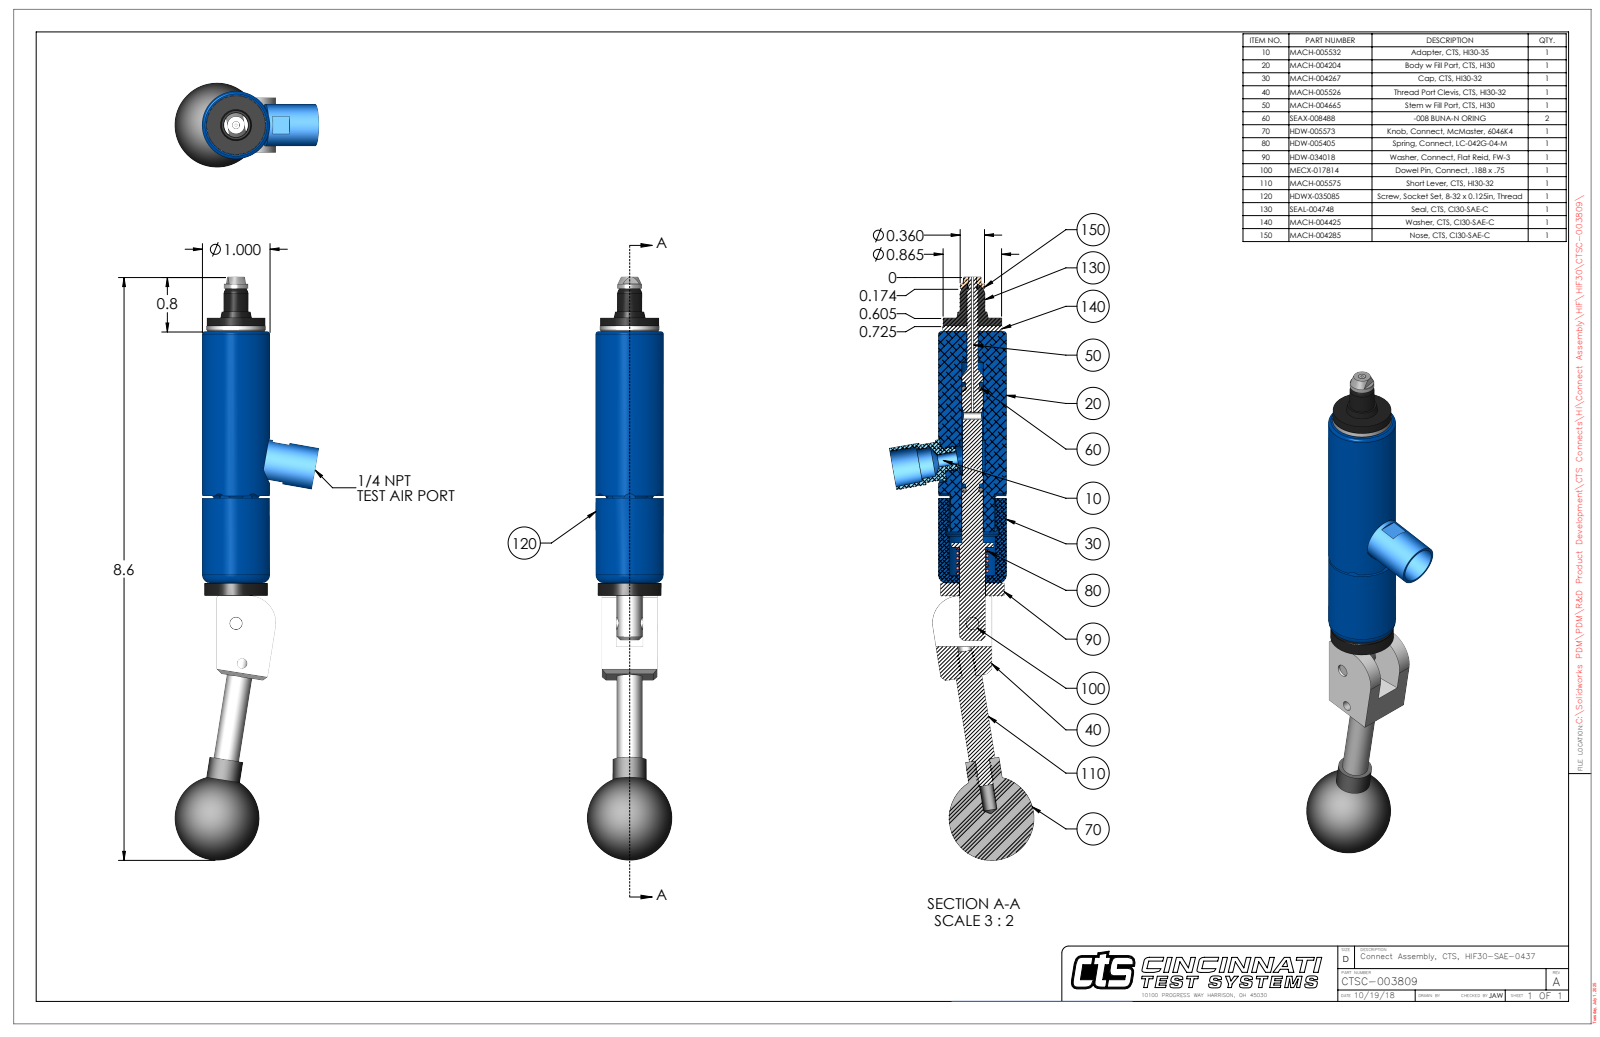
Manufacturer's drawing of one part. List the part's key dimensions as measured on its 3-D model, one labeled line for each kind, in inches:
Part name (STEP PRODUCT): CTSC-003809
STEP written by: SolidWorks 2023 (AUTOMOTIVE_DESIGN)
Units: inches
Bodies: 10 solids, 293 faces (106 planar, 121 cylindrical, 66 other)
Overall size (bounding box): 8.618 × 2.128 × 1.25
Volume: 5.091 in³ · Surface area: 39.38 in²
Round holes (diameter × count): ⌀0.201 ×2, ⌀0.04 ×1, ⌀0.099 ×1, ⌀0.113 ×1, ⌀0.136 ×1, ⌀0.15 ×1, ⌀0.155 ×1, ⌀0.161 ×1, ⌀0.164 ×1, ⌀0.187 ×1, ⌀0.189 ×1, ⌀0.385 ×1
Round bosses / shafts (diameter × count): ⌀1 ×1, ⌀0.936 ×1, ⌀0.875 ×1, ⌀0.865 ×1, ⌀0.62 ×1, ⌀0.5 ×1, ⌀0.38 ×1, ⌀0.375 ×1
Partial cylindrical surfaces — rounded edges, fillets, slot ends (radius × count): R0.093 ×6, R0.015 ×1, R0.054 ×1, R0.325 ×1, R0.4 ×1, R0.457 ×1
Main face-to-face distances: 0.21, 0.602, 0.08, 3.795, 3.715, 0.812, 3.983, 3.903, 0.187, 0.391
Hole centre spacings: 0.599, 1.658, 2.252
